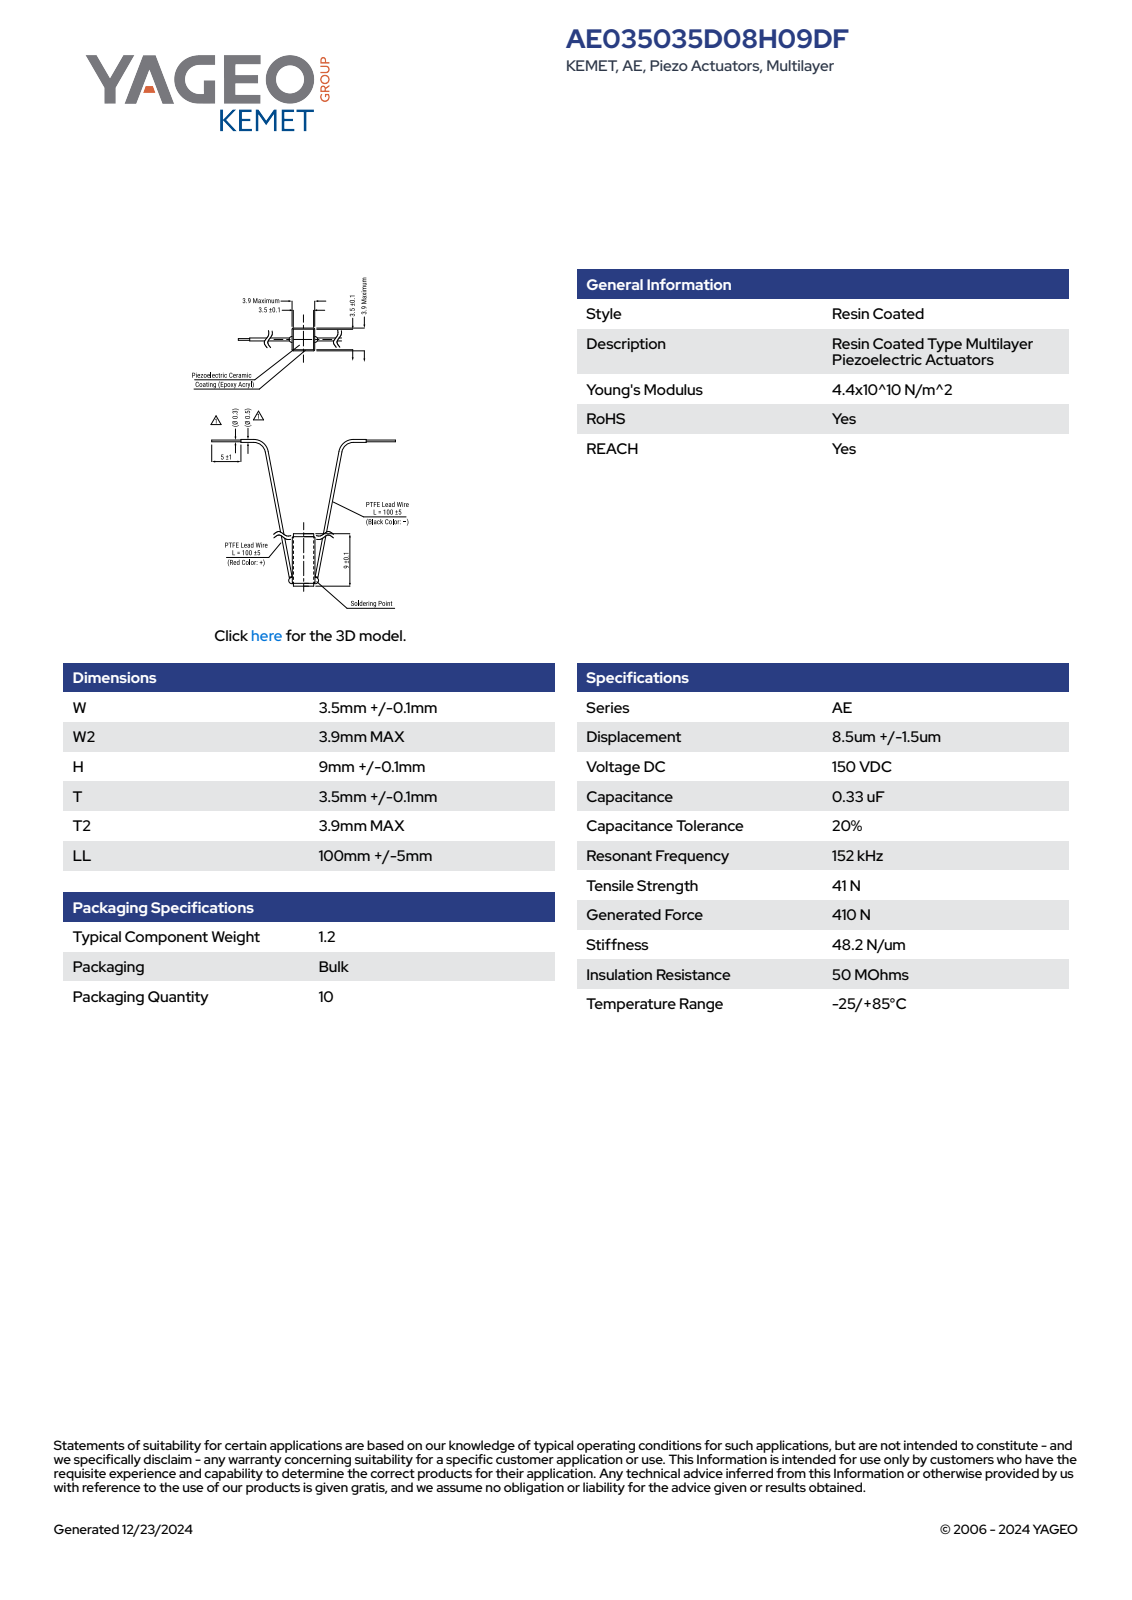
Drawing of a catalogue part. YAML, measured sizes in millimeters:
part_name: "AL_KAE1_W3.6W23.9H9.1T3.6T23.9"
step_written_by: "SolidWorks 2014 (AUTOMOTIVE_DESIGN)"
units: millimeters
bodies: {solids: 4, faces: 93, planar: 85, cylindrical: 8, other: 0}
overall_size: [9.11, 3.9, 3.9]
volume: 118
surface_area: 168
partial_cylinders:
  - {radius: 0.15, count: 8}
face_to_face_distances: [3.6, 3.5, 3.75, 3.4, 9.1, 3.9, 0.89, 3.66, 5.44, 8.21]
